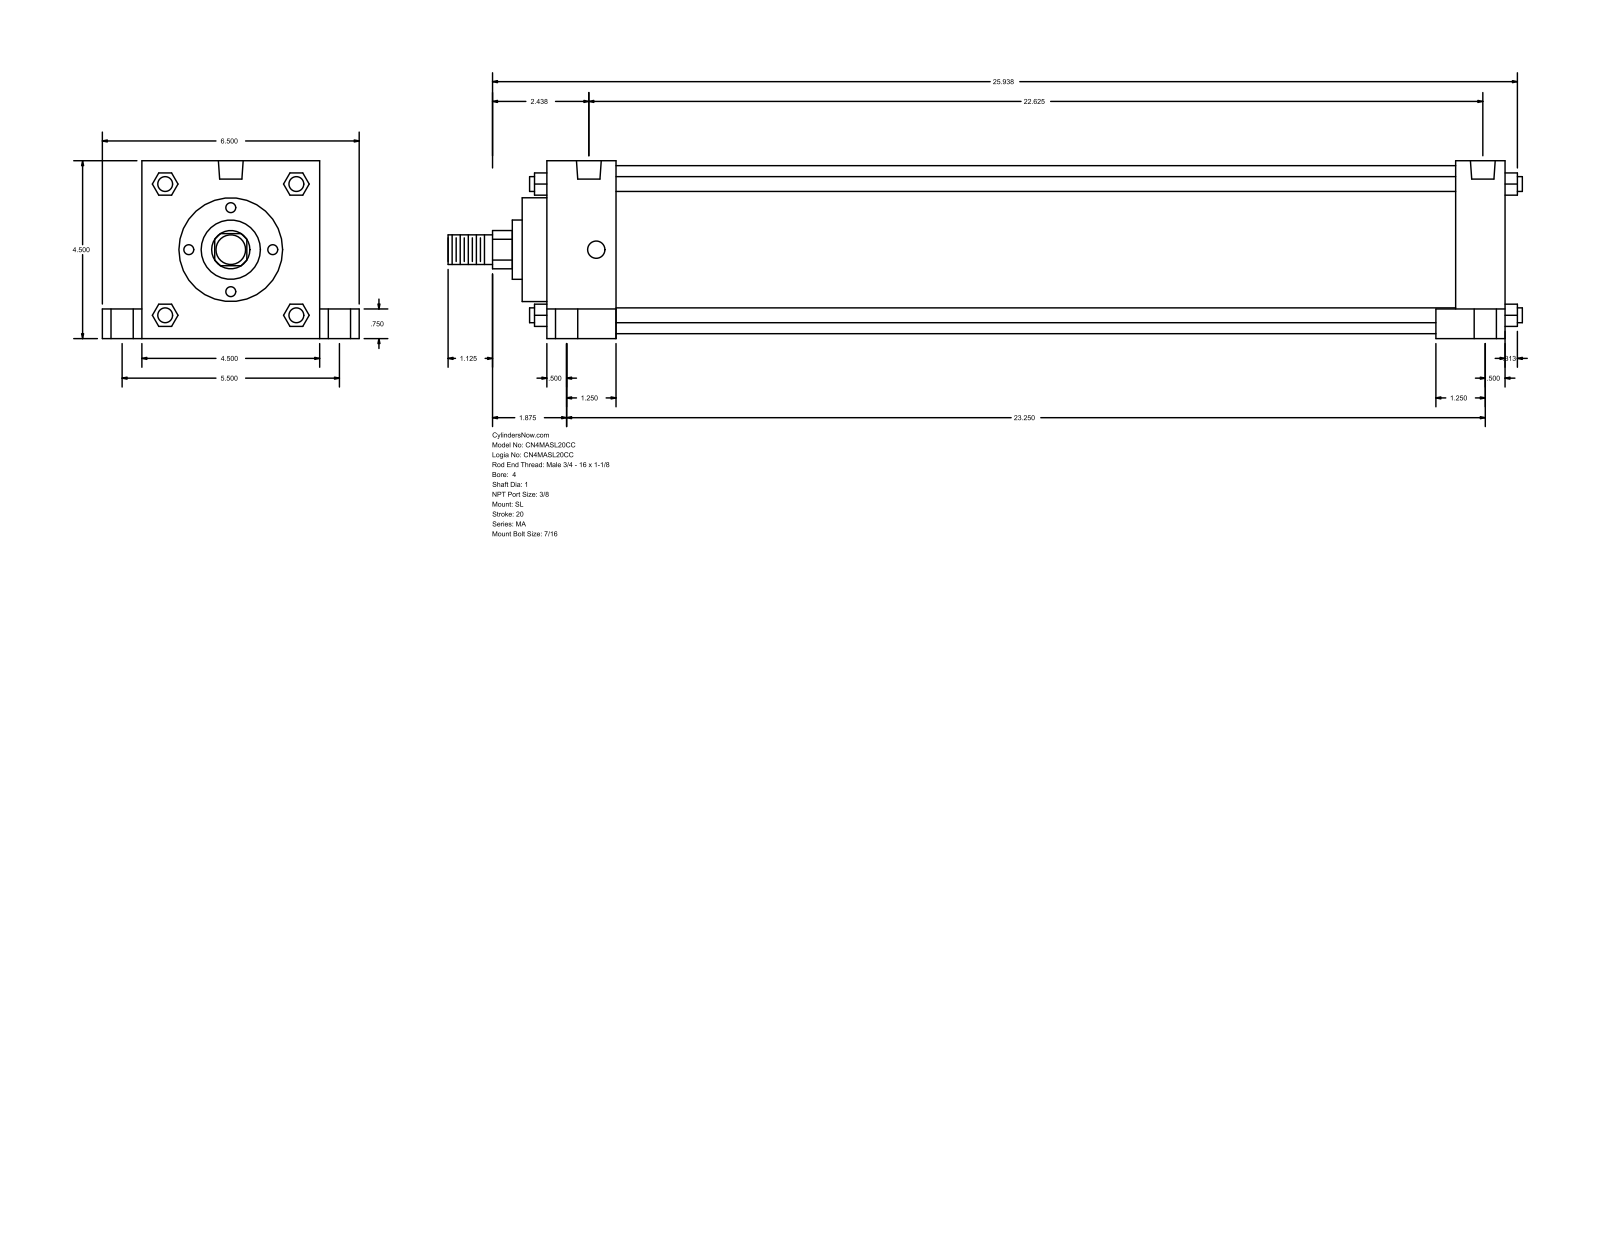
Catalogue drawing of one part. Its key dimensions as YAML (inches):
part_name: "MA_SL__0400_1"
step_written_by: "GSSL Pune (CONFIG_CONTROL_DESIGN)"
units: inches
bodies: {solids: 0, faces: 150, planar: 113, cylindrical: 37, other: 0}
overall_size: [27.187, 6.5, 4.5]
round_holes:
  - {diameter: 0.437, count: 4}
  - {diameter: 0.563, count: 4}
  - {diameter: 0.813, count: 4}
  - {diameter: 0.627, count: 2}
round_bosses_or_shafts:
  - {diameter: 0.375, count: 4}
  - {diameter: 4.25, count: 1}
  - {diameter: 2.625, count: 1}
  - {diameter: 1.5, count: 1}
  - {diameter: 1, count: 1}
  - {diameter: 0.75, count: 1}
partial_cylinders:
  - {radius: 0.484, count: 1}
face_to_face_distances: [4.5, 24.25, 1.75, 22.5, 23, 21.25, 1.25, 1, 5.5, 0.75]
hole_center_spacings: [0.187, 2.751, 2.761, 2.807, 2.85, 5.5, 22.25, 22.438]
